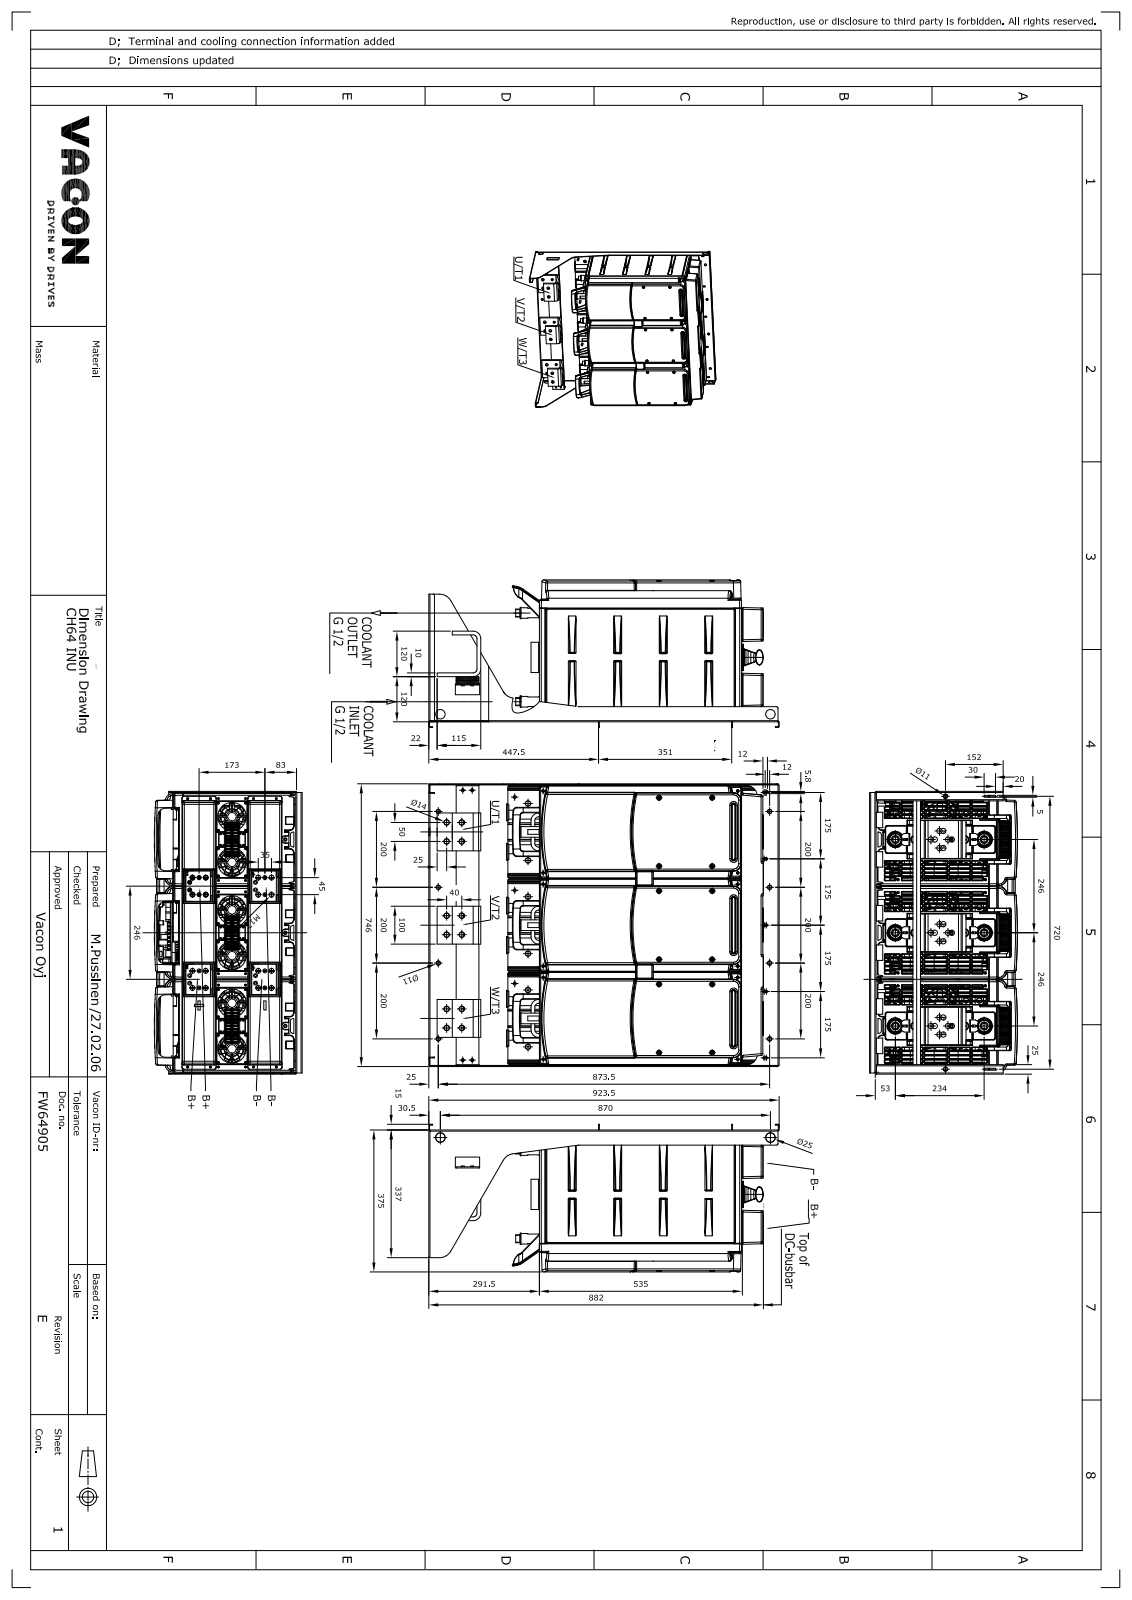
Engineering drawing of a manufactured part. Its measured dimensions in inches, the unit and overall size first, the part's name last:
Units: inches
Overall size (bounding box): 36.358 × 29.37 × 15.338
Round holes (diameter × count): ⌀0.335 ×48, ⌀0.551 ×48, ⌀0.217 ×16, ⌀0.433 ×16, ⌀0.512 ×16, ⌀0.205 ×8, ⌀0.984 ×8, ⌀0.194 ×4, ⌀0.276 ×4, ⌀0.315 ×3, ⌀0.236 ×1
Round bosses / shafts (diameter × count): ⌀1.102 ×6, ⌀0.825 ×6, ⌀0.315 ×4
Partial cylindrical surfaces — rounded edges, fillets, slot ends (radius × count): R0.114 ×10, R0.197 ×8, R0.256 ×6, R59.054 ×3, R0.787 ×2, R1.181 ×2, R1.769 ×2, R1.378 ×1
Main face-to-face distances: 0.079, 9.685, 9.592, 19.37, 19.277, 0.093, 6.831, 2.618, 0.118, 2.971
Hole centre spacings: 9.685, 0.689, 1.901, 6.831, 11.852, 1.772, 1.969, 19.37
Volume: 9 056 in³ · Surface area: 7 981 in²
Bodies: 1 solid, 1660 faces (1173 planar, 472 cylindrical, 15 other)
Part name (STEP PRODUCT): PRT0001
STEP written by: CREO PARAMETRIC BY PTC INC, 2018070 (CONFIG_CONTROL_DESIGN)
